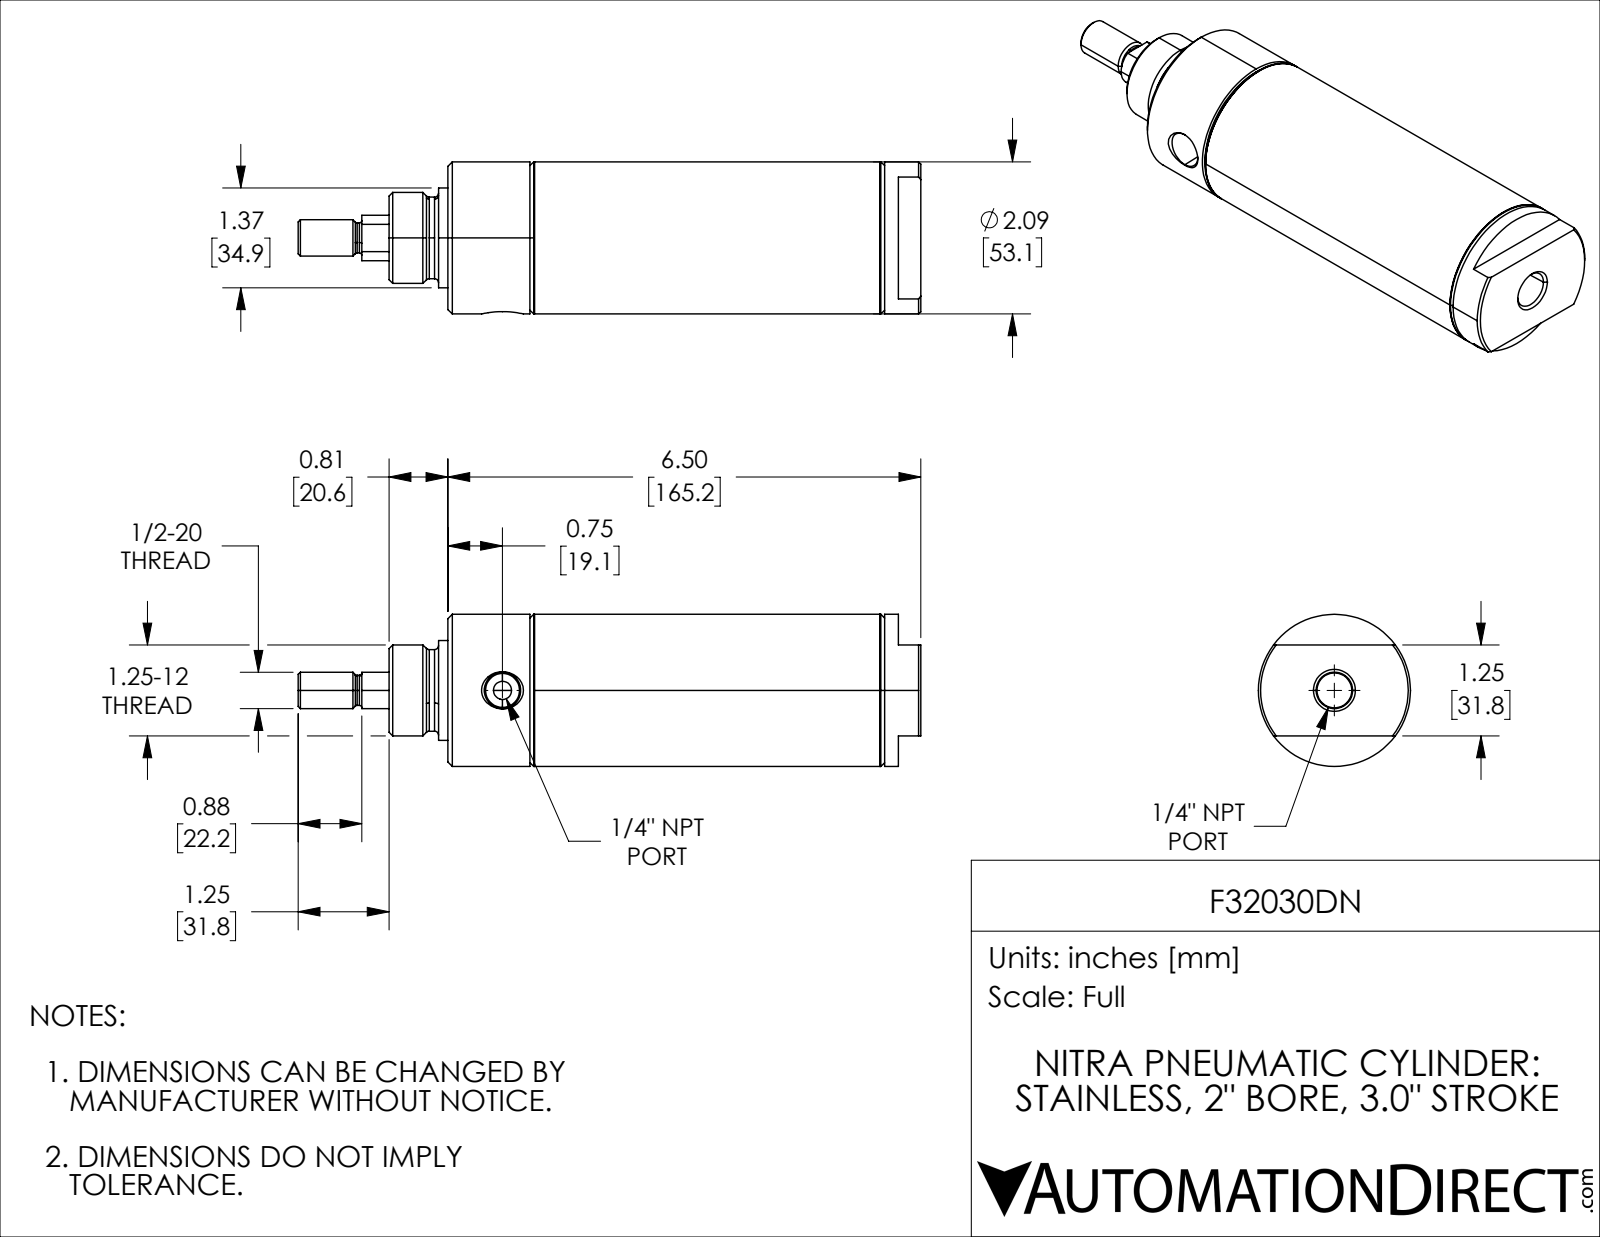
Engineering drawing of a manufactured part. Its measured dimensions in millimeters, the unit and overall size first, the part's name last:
Units: millimetres
Overall size (bounding box): 217.47 × 53.09 × 53.09
Round holes (diameter × count): ⌀6.35 ×1, ⌀12.18 ×1, ⌀16.52 ×1, ⌀31.75 ×1, ⌀49.05 ×1
Round bosses / shafts (diameter × count): ⌀53.09 ×1, ⌀51.16 ×1, ⌀34.87 ×1, ⌀28.51 ×1, ⌀15.88 ×1, ⌀12.7 ×1, ⌀10.46 ×1
Main face-to-face distances: 30.17, 76.2, 106.37, 127, 50.8, 20.63, 106.38, 30.18, 20.62, 38.15
Volume: 228 111 mm³ · Surface area: 84 037 mm²
Bodies: 4 solids, 133 faces (25 planar, 46 cylindrical, 62 other)
Part name (STEP PRODUCT): F32030DN_3; F32030DN; F32030DN_9; F32030DN_7 (+1 more)
STEP written by: SolidWorks 2021 (CONFIG_CONTROL_DESIGN)
